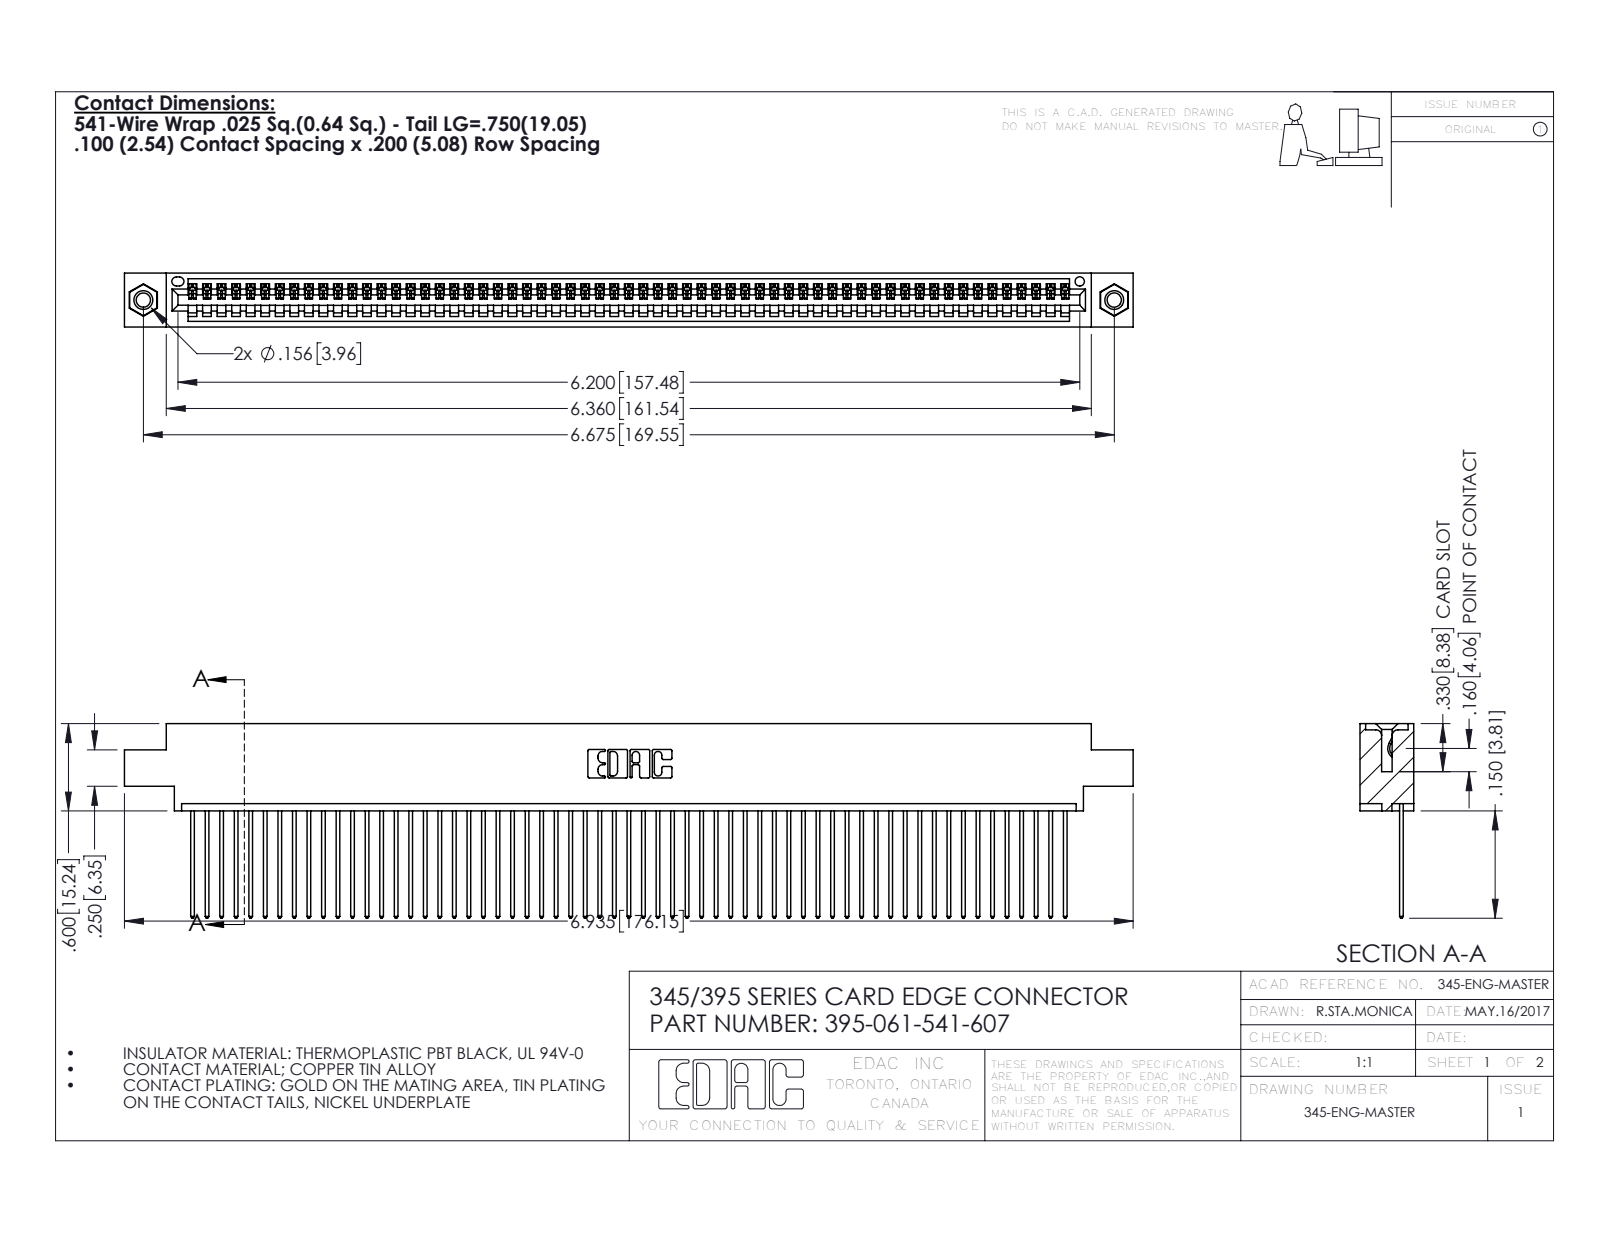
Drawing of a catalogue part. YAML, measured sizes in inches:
part_name: "395-061-541-607; 345 Part_0.170 Offset - 0.156 Dia-TI; 345-250-001_345-250-005-103; 345-292-001_345-293-141"
step_written_by: "SolidWorks 2016 (CONFIG_CONTROL_DESIGN)"
units: inches
bodies: {solids: 64, faces: 3728, planar: 2556, cylindrical: 1156, other: 16}
overall_size: [6.935, 1.337, 0.37]
volume: 1.035
surface_area: 37.42
round_holes:
  - {diameter: 0.098, count: 2}
  - {diameter: 0.125, count: 2}
  - {diameter: 0.156, count: 2}
  - {diameter: 0.064, count: 1}
round_bosses_or_shafts:
  - {diameter: 0.155, count: 2}
partial_cylinders:
  - {radius: 0.006, count: 122}
  - {radius: 0.01, count: 122}
  - {radius: 0.01, count: 22}
  - {radius: 0.007, count: 6}
  - {radius: 0.031, count: 6}
  - {radius: 0.026, count: 3}
  - {radius: 0.031, count: 2}
  - {radius: 0.04, count: 2}
face_to_face_distances: [0.072, 0.298, 0.098, 0.272, 0.025, 0.37, 0.2, 0.225, 0.175, 0.149]
hole_center_spacings: [0.27, 6.439, 6.675]
